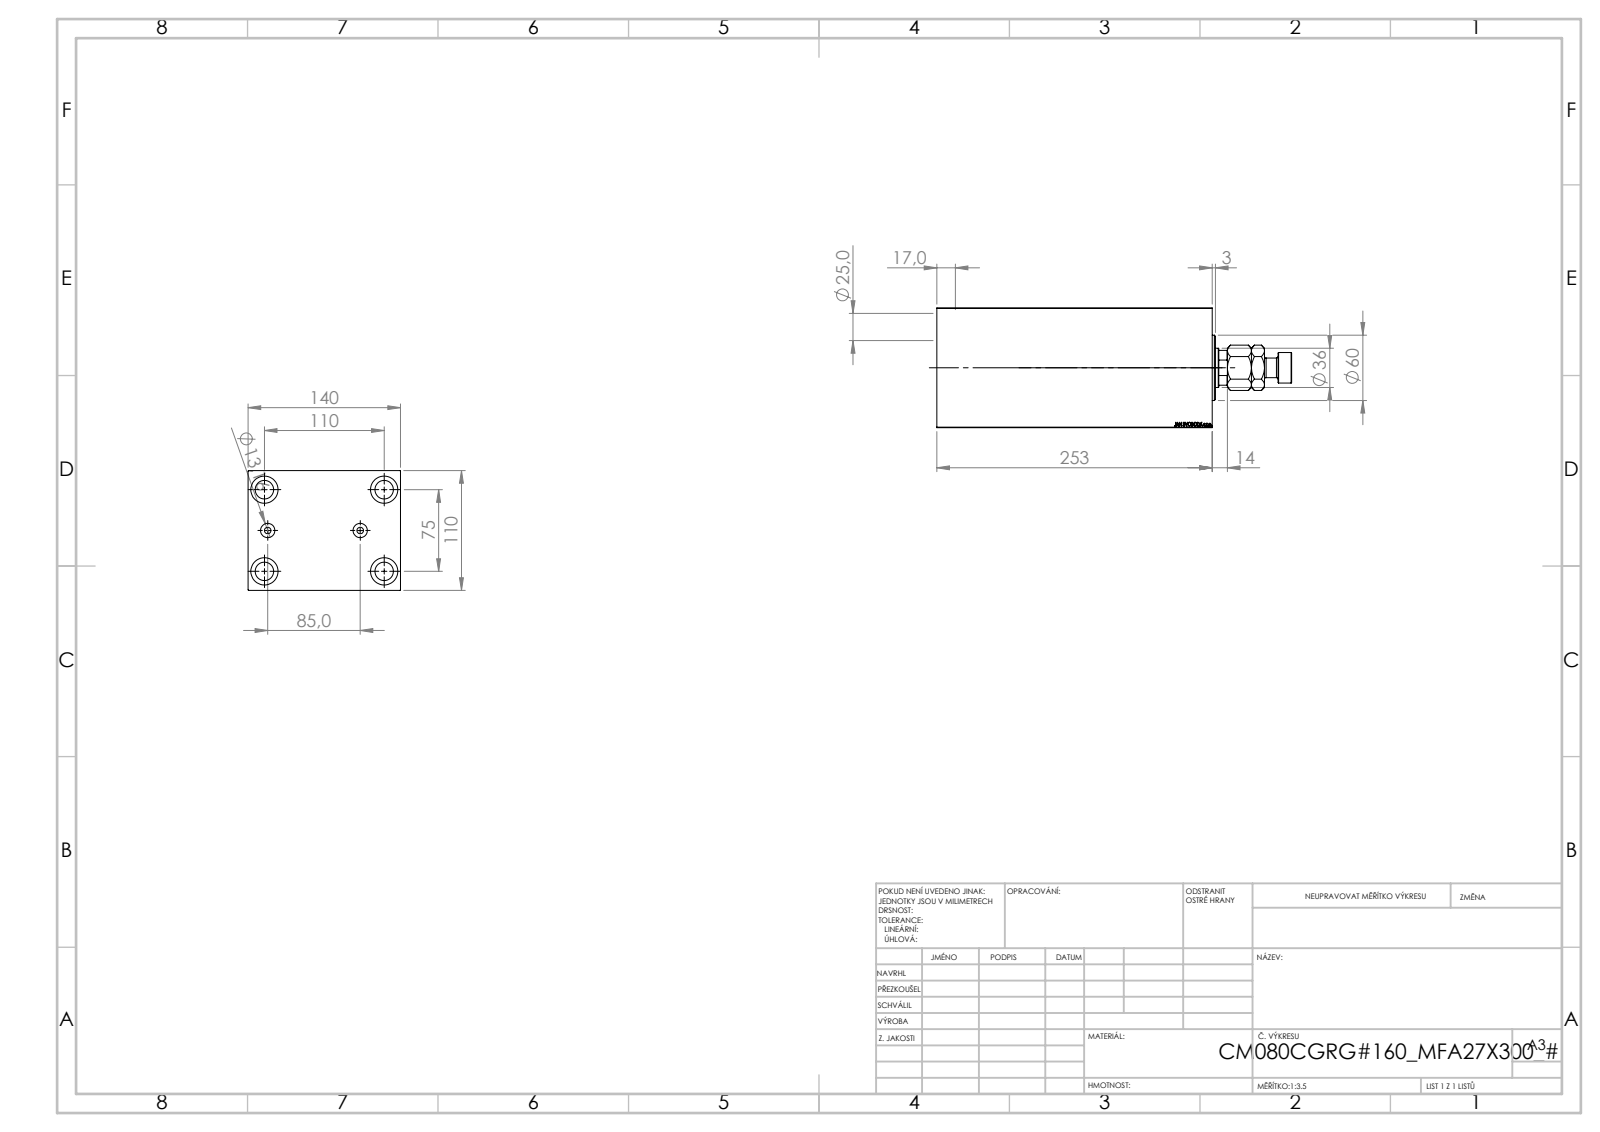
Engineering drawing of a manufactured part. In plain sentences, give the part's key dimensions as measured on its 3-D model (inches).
The part is named "V450CM_C_VCP; V450CM_C_Body; V450CM_VC_B; MFA". Its 3-D file was written by "SolidWorks 2019 (CONFIG_CONTROL_DESIGN)". It is 4 solids with 915 faces: 427 planar, 62 cylindrical and 426 other. Overall it measures 12.835 by 5.512 by 4.331 inches. Its volume is 184.5 cubic inches and its surface area 552.2 square inches. Round holes: 4 of diameter 0.669, 4 of diameter 0.984, 2 of diameter 0.236, 2 of diameter 0.518, 1 of diameter 1.004, 1 of diameter 1.417, 1 of diameter 1.555, 1 of diameter 3.15, 1 of diameter 3.228, 1 of diameter 3.425. Round bosses or shafts: 1 of diameter 2.362, 1 of diameter 1.102, 1 of diameter 0.709. Partial cylindrical surfaces (rounded edges, fillets, slot ends): 1 of radius 0.689. The main face-to-face distances are 4.331, 5.512, 9.961, 9.134, 0.827, 1.469, 7.665, 8.492, 7.768, 6.299. The hole center spacings are 1.556, 2.621, 4.113, 1.673, 2.953, 4.331, 5.242, 3.346.
